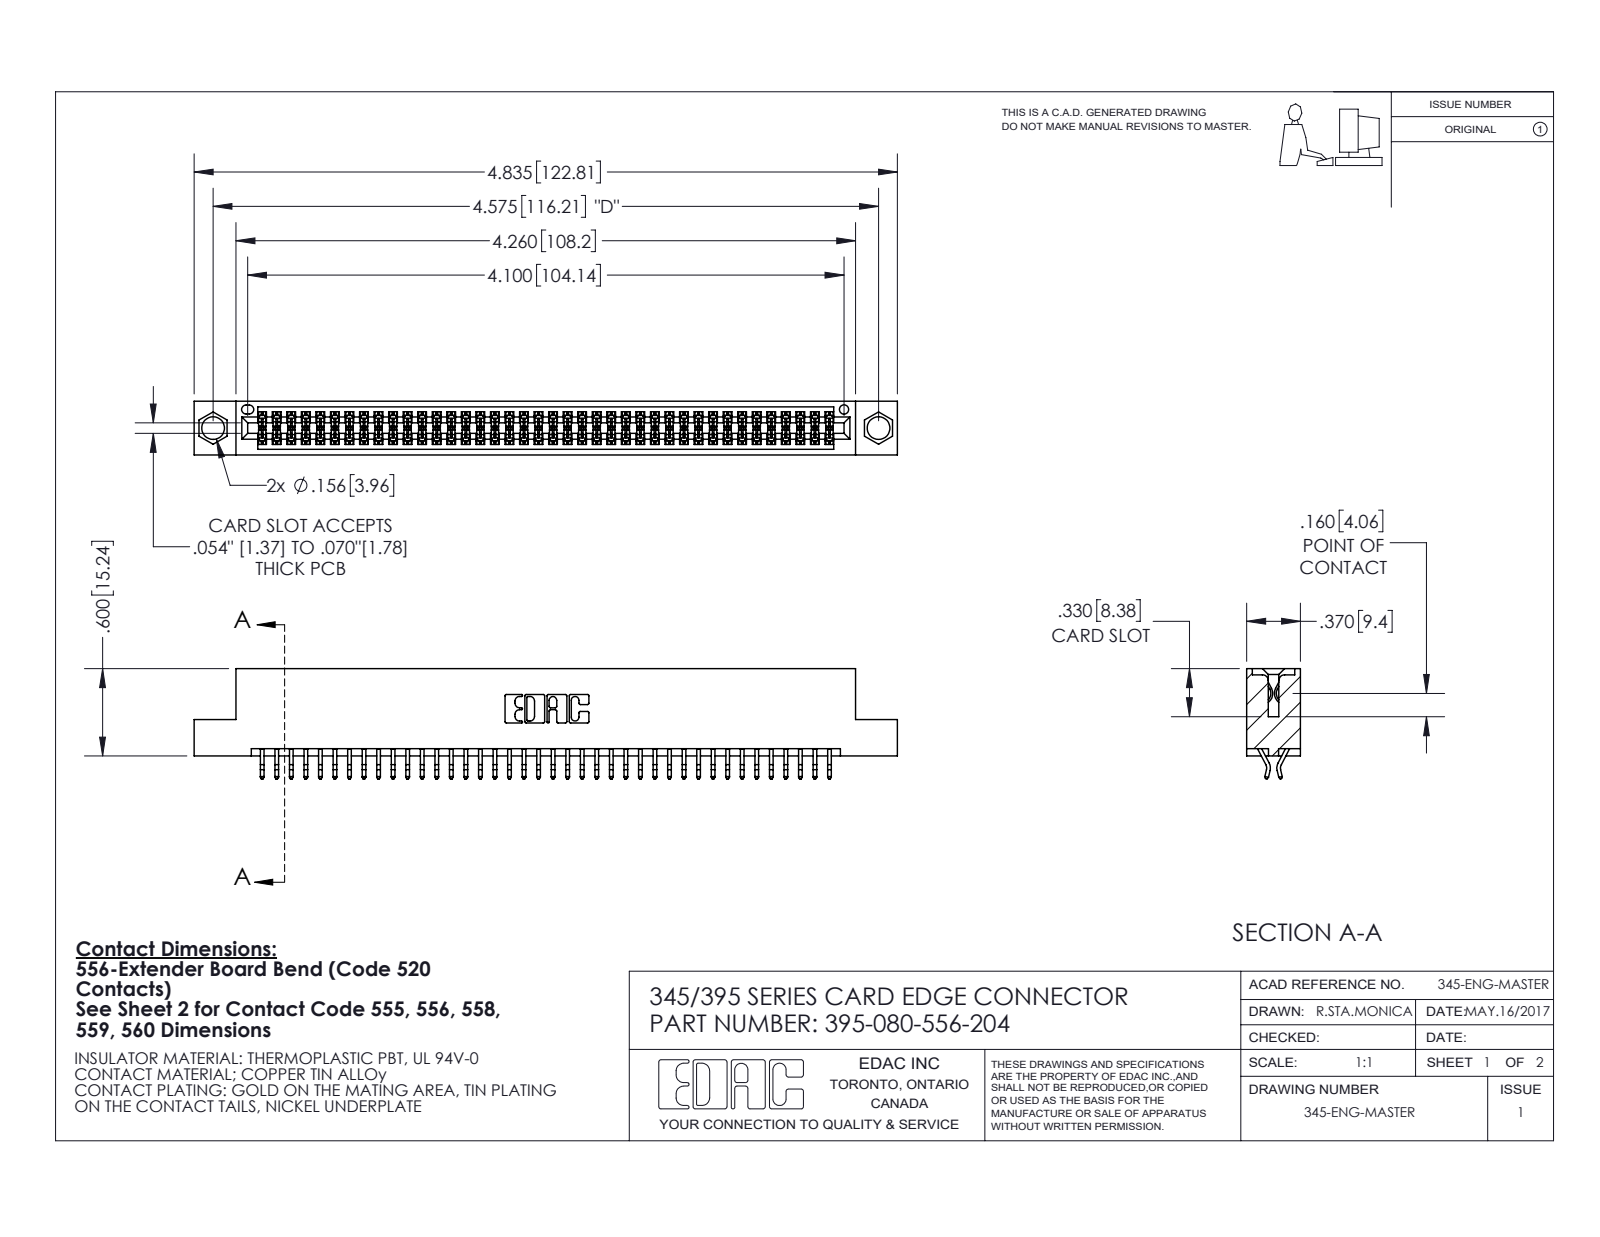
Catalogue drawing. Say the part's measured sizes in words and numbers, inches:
The part is named "345 Part_Flush Mounting Lugs - 0.156 Dia-TI; 345-292-001_556 Tail; 395-080-556-204". Its 3-D file was written by "SolidWorks 2020 (CONFIG_CONTROL_DESIGN)". It is 81 solids with 4620 faces: 3054 planar, 1566 cylindrical and 0 other. Overall it measures 4.835 by 0.757 by 0.37 inches. Its volume is 0.72 cubic inches and its surface area 26.64 square inches. Round holes: 2 of diameter 0.156, 1 of diameter 0.064. Partial cylindrical surfaces (rounded edges, fillets, slot ends): 160 of radius 0.006, 22 of radius 0.01, 6 of radius 0.007, 6 of radius 0.031, 3 of radius 0.026, 2 of radius 0.01, 2 of radius 0.014, 2 of radius 0.019. The main face-to-face distances are 0.298, 0.072, 0.37, 0.2, 0.025, 0.098, 0.272, 0.225, 0.175, 0.149. The hole center spacings are 0.27, 4.339, 4.575.
